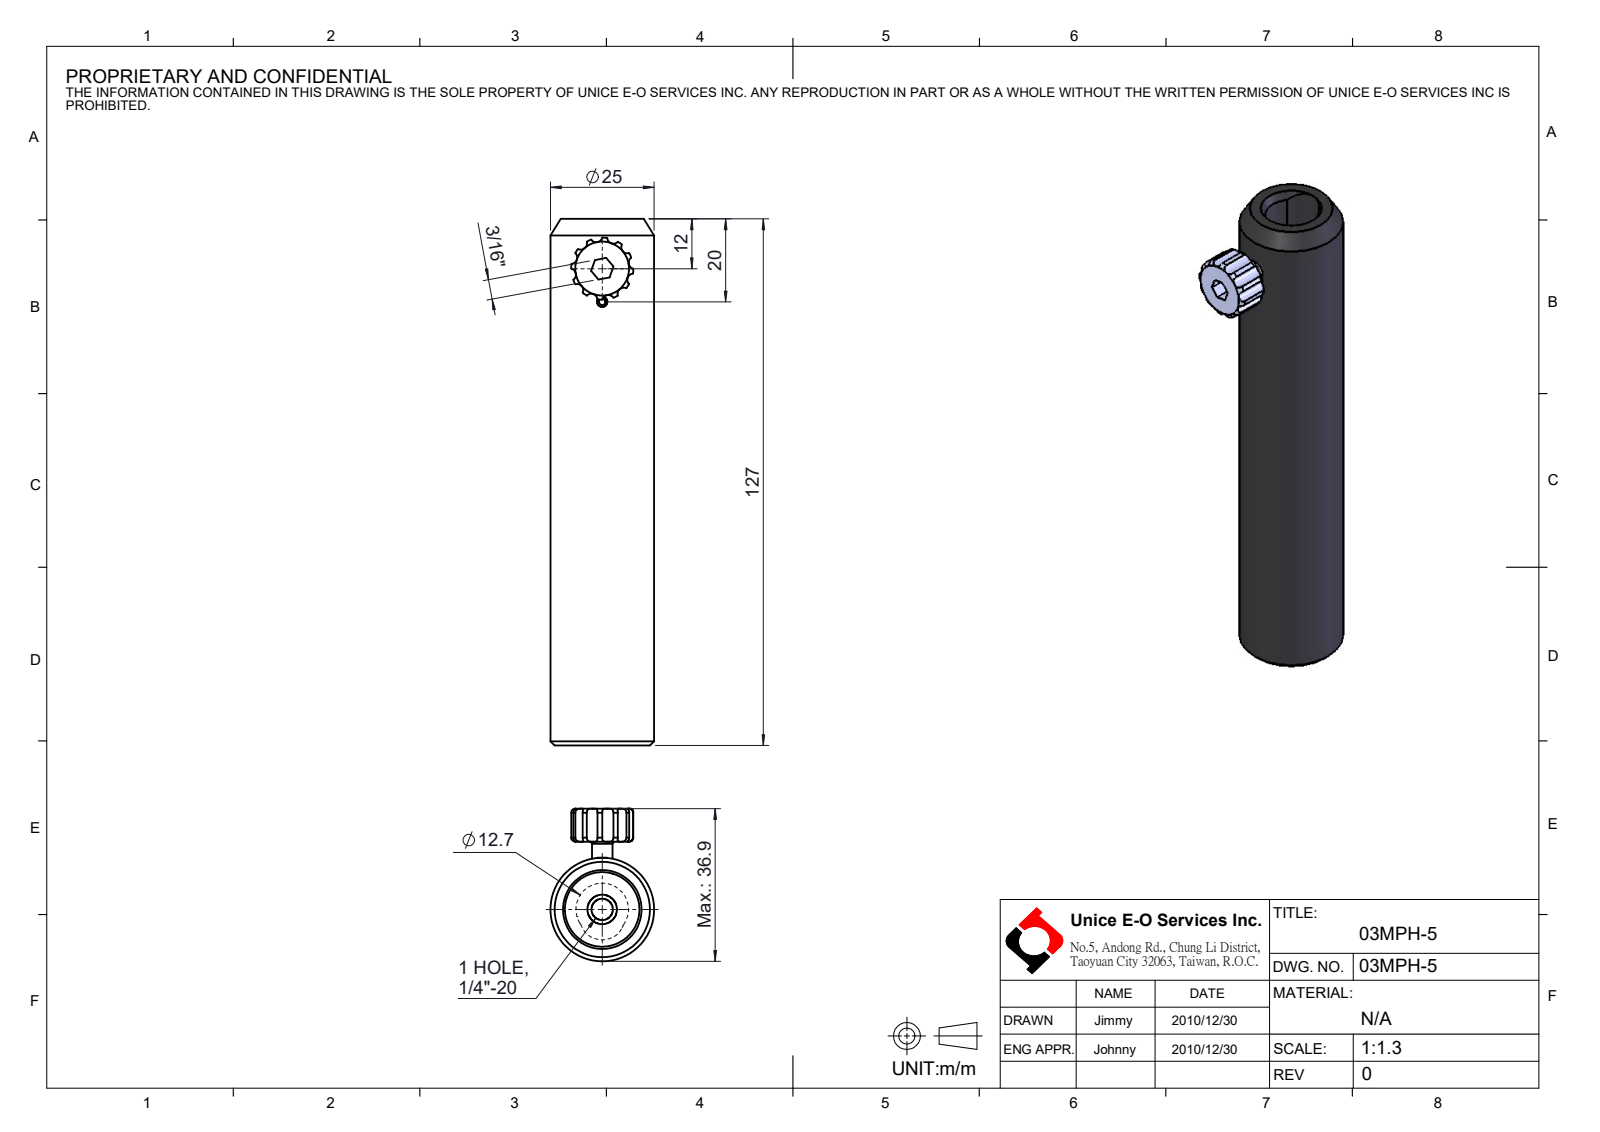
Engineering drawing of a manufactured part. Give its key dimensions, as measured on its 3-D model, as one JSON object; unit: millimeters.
{"part_name": "03MPH-5", "step_written_by": "SolidWorks 2016 (CONFIG_CONTROL_DESIGN)", "units": "millimeters", "bodies": {"solids": 0, "faces": 96, "planar": 16, "cylindrical": 42, "other": 38}, "overall_size": [127, 36.85, 25], "round_holes": [[2.5, 1], [5.11, 1], [19, 1]], "round_bosses_or_shafts": [[25, 1], [4.94, 1]], "partial_cylinders_radius": [[1.5, 12], [5.5, 1], [6.35, 1], [7.5, 1]], "face_to_face_distances": [127, 8, 4.76, 3.85, 11.85, 1.5]}
